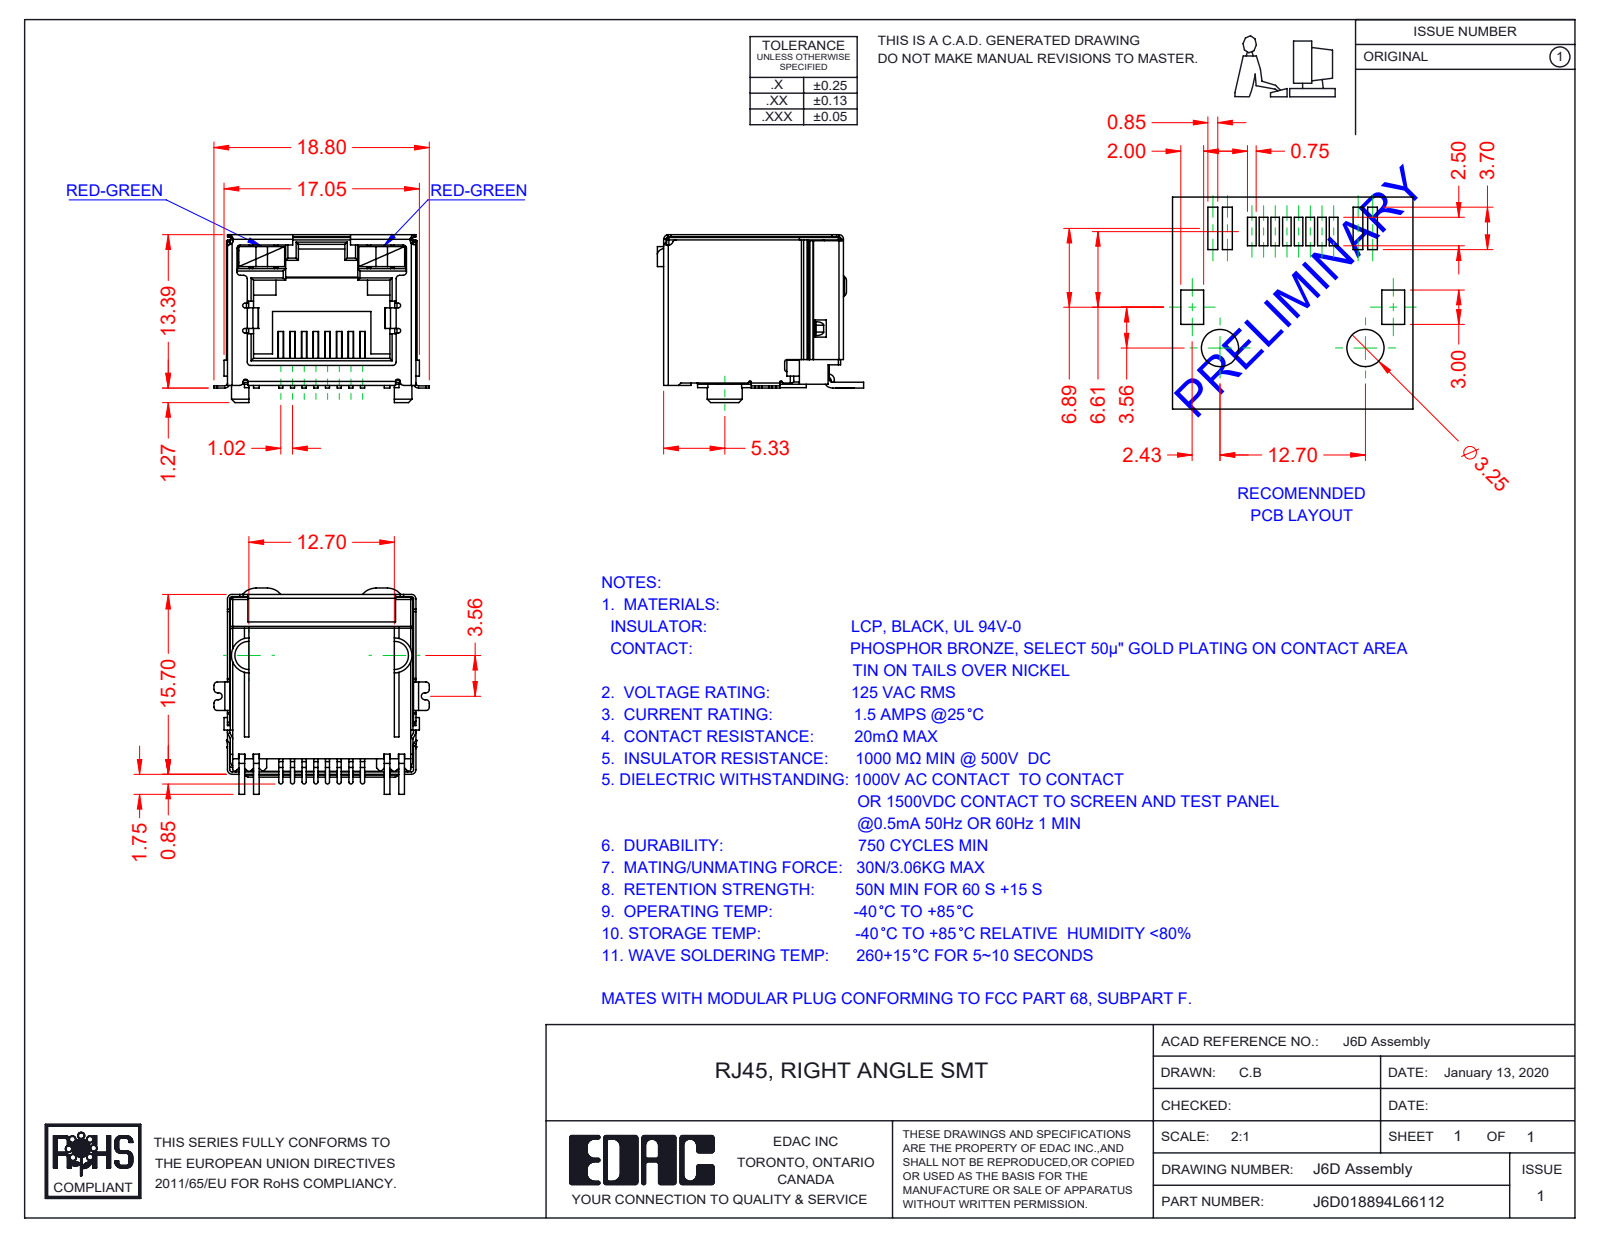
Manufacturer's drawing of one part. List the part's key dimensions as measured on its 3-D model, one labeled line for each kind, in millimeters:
Part name (STEP PRODUCT): 6D Insulator; J6D018894L66112; 6D Shield_LED - No EMI; 6D LED RH_6-Red-Green (+2 more)
STEP written by: SolidWorks 2016 (CONFIG_CONTROL_DESIGN)
Units: millimetres
Bodies: 12 solids, 899 faces (646 planar, 220 cylindrical, 33 other)
Overall size (bounding box): 18.8 × 18 × 14.65
Volume: 1 804 mm³ · Surface area: 4 898 mm²
Partial cylindrical surfaces — rounded edges, fillets, slot ends (radius × count): R0.3 ×39, R0.2 ×37, R0.4 ×16, R0.1 ×12, R0.15 ×8, R0.18 ×8, R0.5 ×6, R1.5 ×5
Main face-to-face distances: 16, 16.25, 16.2, 2.25, 1, 15.95, 16.05, 12.8, 0.45, 16.45
